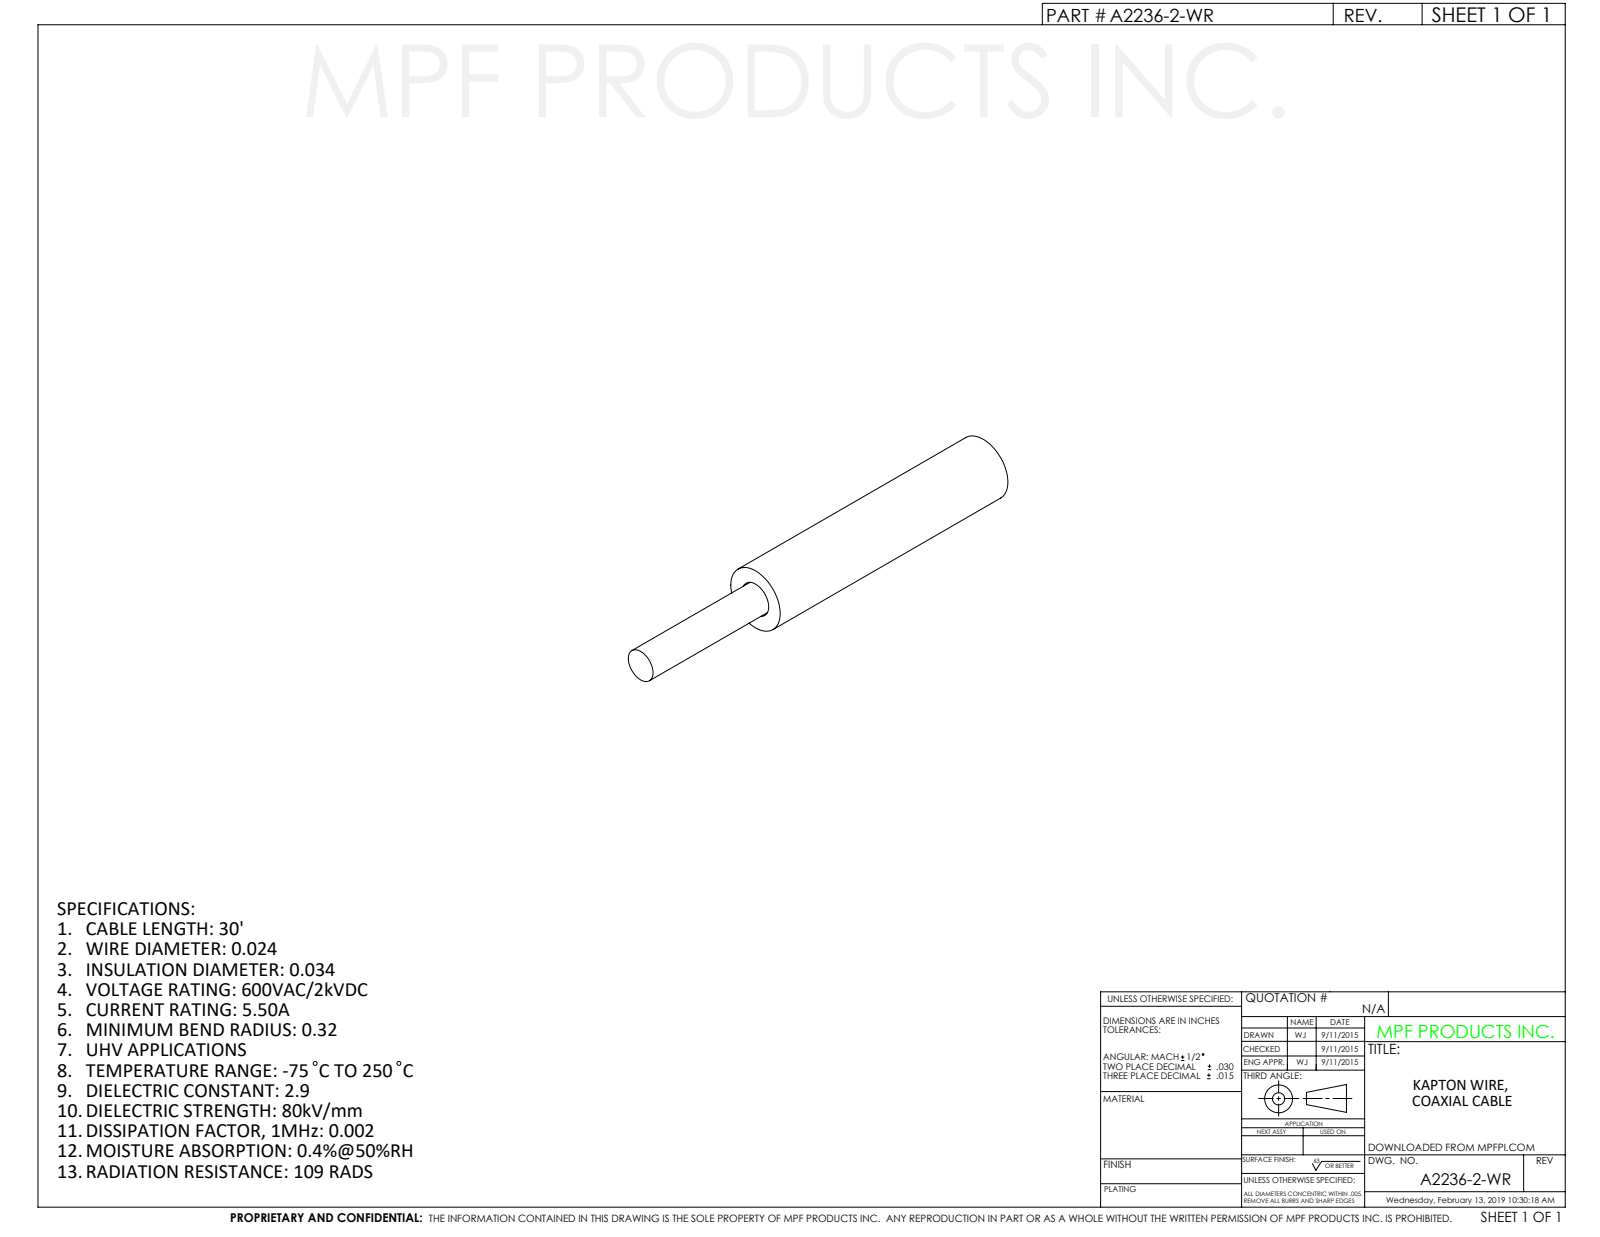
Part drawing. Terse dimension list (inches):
name: A2236-2-WR
written by: SolidWorks 2012 (CONFIG_CONTROL_DESIGN)
unit: in
bodies: 2 solids, 11 faces (3 planar, 6 cylindrical, 2 other)
size: 0.14 × 0.02 × 0.02
holes: 1× ⌀0.011
bosses: 1× ⌀0.02, 1× ⌀0.01
face distances: 0.092
